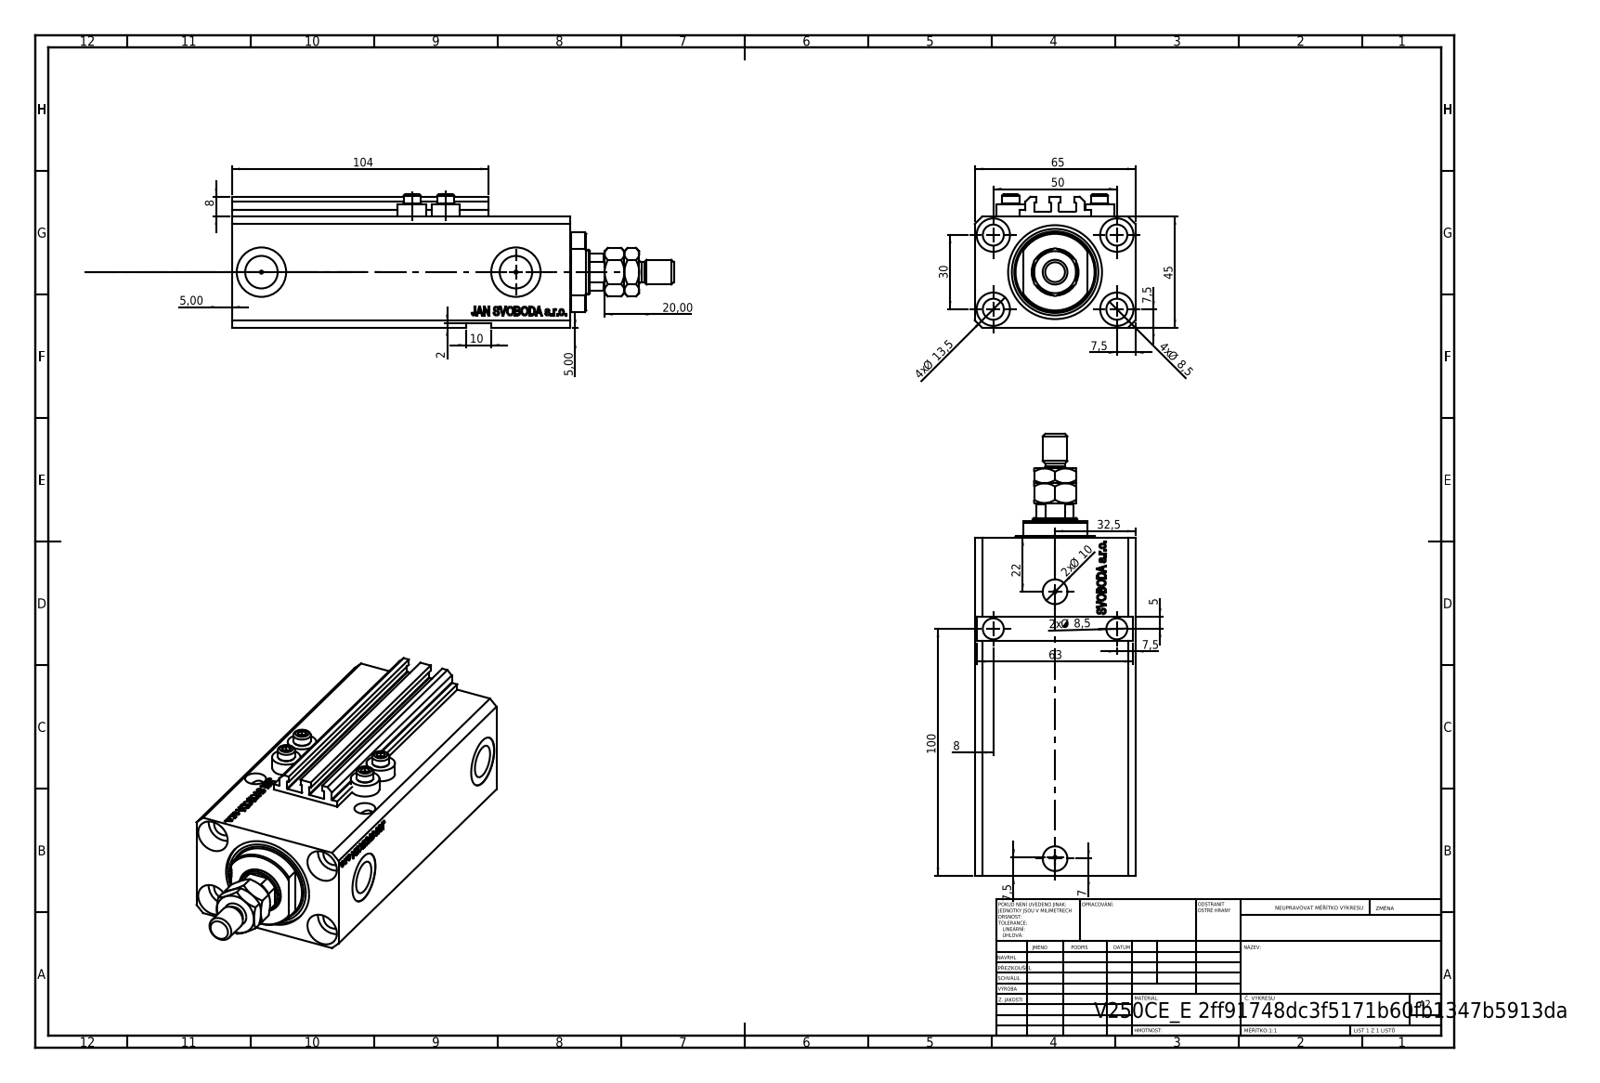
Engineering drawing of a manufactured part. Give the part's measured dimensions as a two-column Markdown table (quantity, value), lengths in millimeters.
| quantity | value |
| --- | --- |
| part name | V250CE_C_VCP; V250CE_VC_E; V250CE_E_Body; MTA (+1 more) |
| STEP written by | SolidWorks 2019 (CONFIG_CONTROL_DESIGN) |
| units | millimeters |
| bodies | 9 solids, 1132 faces (530 planar, 142 cylindrical, 460 other) |
| overall size | 178.9 × 65 × 54 |
| volume | 354 831 mm³ |
| surface area | 97 480 mm² |
| round holes (diameter × count) | 8.5 × 7, 1.25 × 4, 4 × 4, 13.5 × 4, 10 × 2, 13.16 × 2, 20 × 2, 18 × 1, 25 × 1, 38 × 1 |
| round bosses / shafts (diameter × count) | 11.6 × 4, 7 × 4, 10 × 1, 8 × 1 |
| partial cylindrical surfaces (radius × count) | 0.2 × 10, 8.5 × 1, 16 × 1 |
| main face-to-face distances | 45, 65, 2, 47, 111.9, 2.5, 10, 24, 20.4, 6.9 |
| hole center spacings | 29.15, 50, 13.6, 15.12, 27.89, 30, 33.62, 36 |
